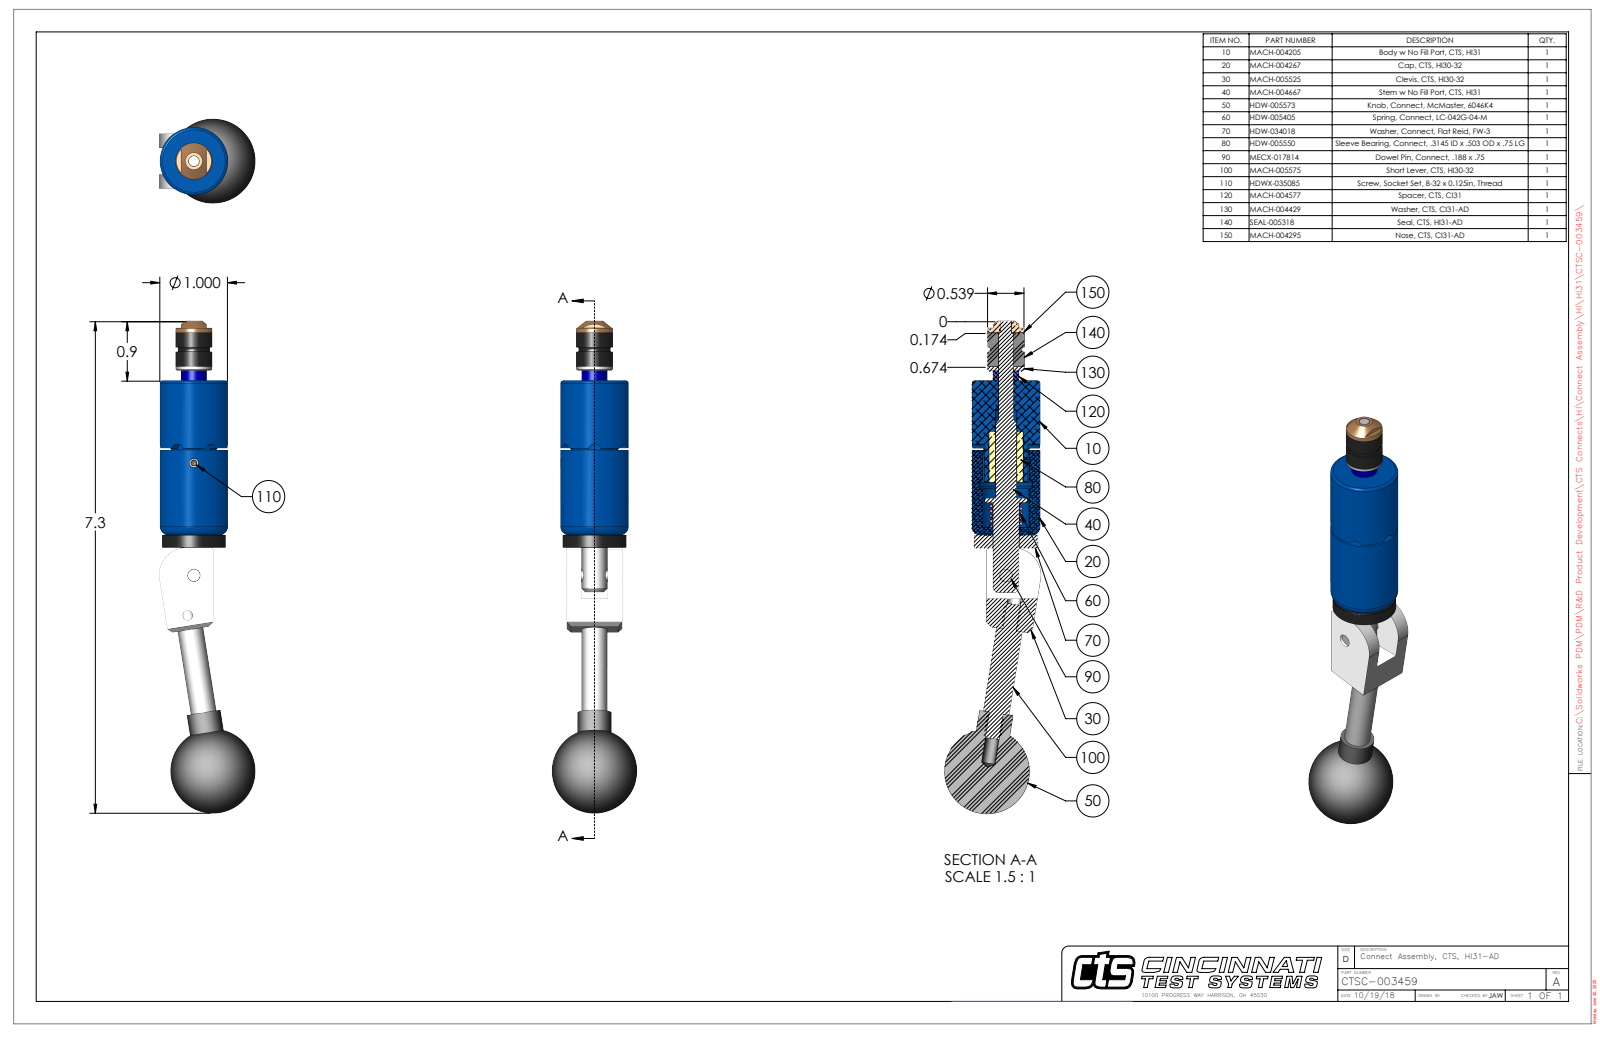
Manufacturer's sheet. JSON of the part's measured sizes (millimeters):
{"part_name": "CTSC-003459", "step_written_by": "SolidWorks 2023 (AUTOMOTIVE_DESIGN)", "units": "millimeters", "bodies": {"solids": 10, "faces": 253, "planar": 98, "cylindrical": 98, "other": 57}, "overall_size": [184.6, 36, 31.8], "volume_mm3": 62630, "surface_area_mm2": 20230, "round_holes": [[5.1, 2], [3.5, 1], [3.8, 1], [4, 1], [4.8, 1], [5.5, 1], [5.8, 1], [5.8, 1], [9.8, 1], [10, 1]], "round_bosses_or_shafts": [[25.4, 1], [23.8, 1], [13.7, 1], [13.7, 1], [12.7, 1], [9.7, 1], [9.6, 1], [9.5, 1]], "partial_cylinders_radius": [[2.4, 6], [0.7, 2], [8.7, 1], [10.2, 1], [12, 1]], "face_to_face_distances": [5.3, 15.3, 20.6, 4.7, 57.9, 62.7, 9.9, 17.9, 75.8, 80.6], "hole_center_spacings": [15.2, 42.1, 57.2]}
